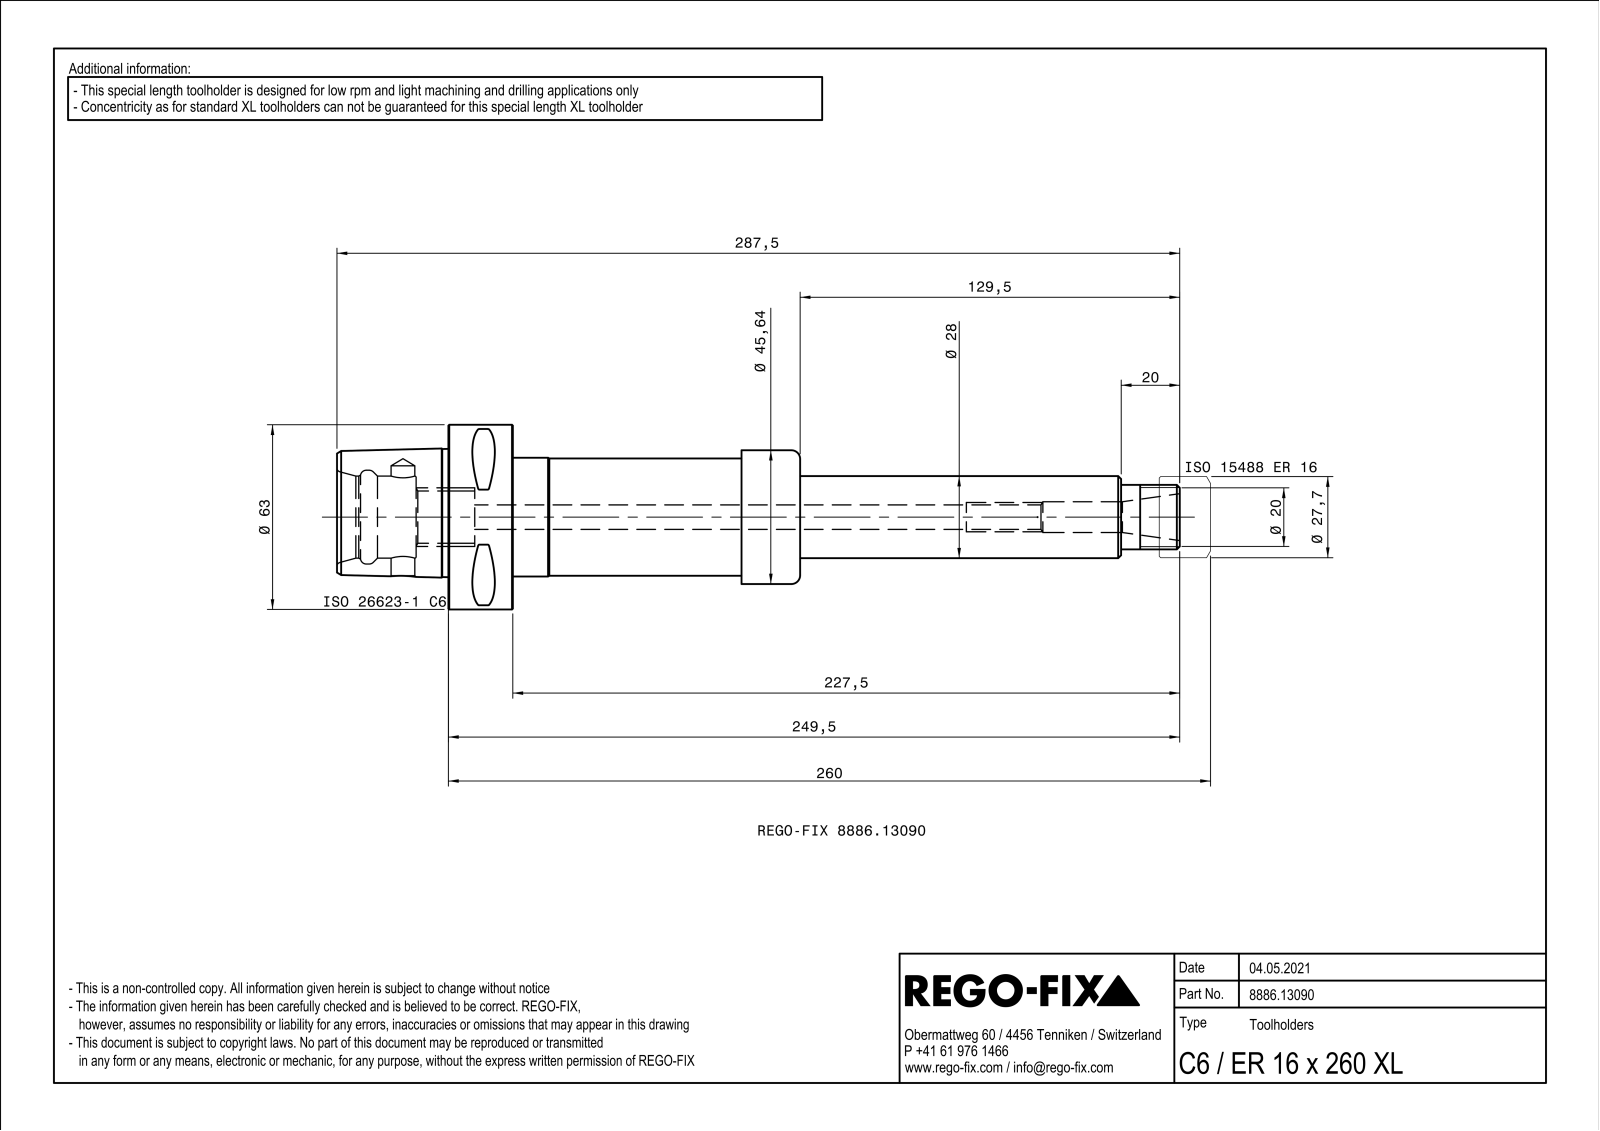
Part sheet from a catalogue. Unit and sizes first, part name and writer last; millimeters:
Units: millimetres
Overall size (bounding box): 287.7 × 63 × 63
Round holes (diameter × count): ⌀4 ×1, ⌀8.1 ×1, ⌀8.35 ×1, ⌀8.38 ×1, ⌀9.6 ×1, ⌀10.5 ×1, ⌀17.84 ×1, ⌀25 ×1, ⌀28 ×1, ⌀32 ×1, ⌀38.38 ×1, ⌀40.05 ×1
Round bosses / shafts (diameter × count): ⌀63 ×1, ⌀45.65 ×1, ⌀40.5 ×1, ⌀40 ×1, ⌀34 ×1, ⌀33.3 ×1, ⌀28.3 ×1, ⌀24.7 ×1
Partial cylindrical surfaces — rounded edges, fillets, slot ends (radius × count): R0.5 ×8
Main face-to-face distances: 22, 98, 120, 6, 14, 158, 60, 38, 20, 1.5
Hole centre spacings: 27.5
Volume: 271 615 mm³ · Surface area: 59 106 mm²
Bodies: 1 solid, 158 faces (31 planar, 33 cylindrical, 94 other)
Part name (STEP PRODUCT): NOCUT
STEP written by: SIEMENS PLM Software Solid Edge ST10 (AUTOMOTIVE_DESIGN)
